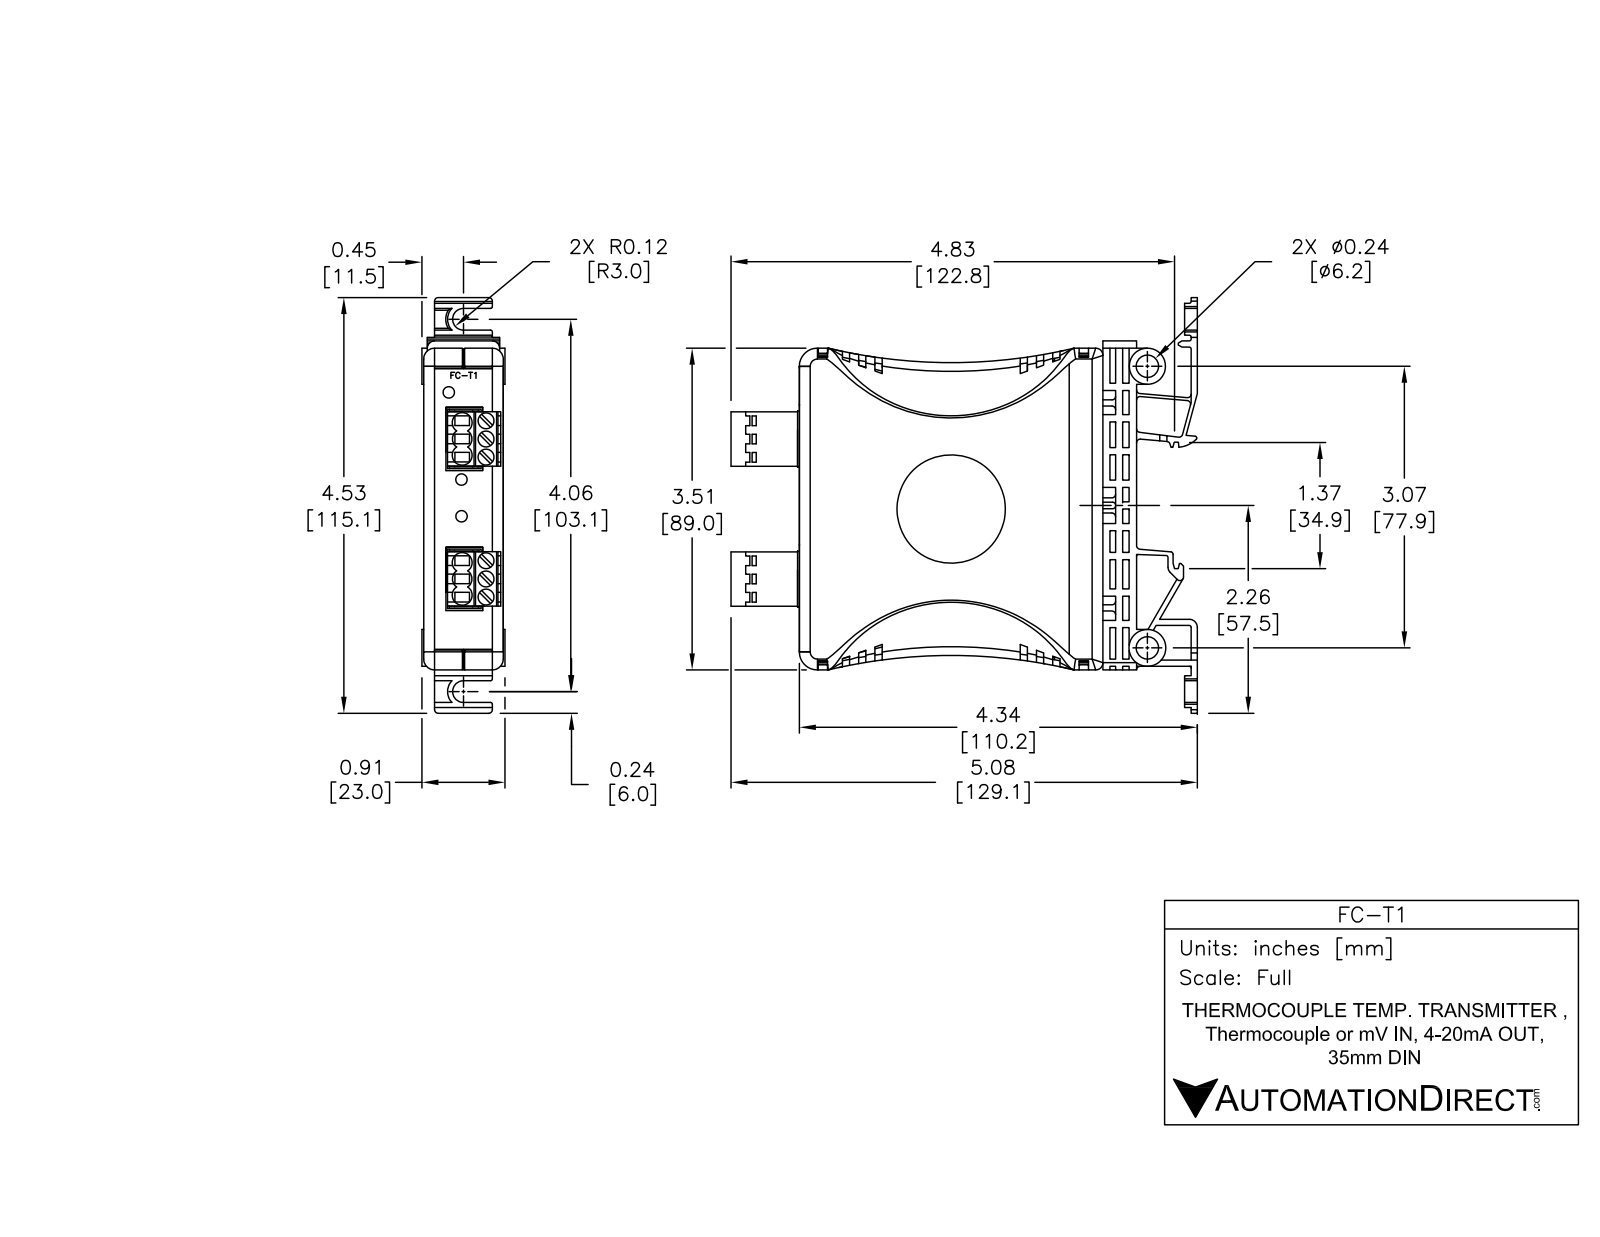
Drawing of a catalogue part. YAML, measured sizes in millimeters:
part_name: "FC-ISO-C r1b Case Only 1 red1 fXT -surf1 - internals COMPLETE FC-T1 pre coord"
step_written_by: "SolidWorks 2017 (AUTOMOTIVE_DESIGN)"
units: millimeters
bodies: {solids: 13, faces: 2341, planar: 1747, cylindrical: 374, other: 220}
overall_size: [115.5, 110.2, 23.6]
volume: 59780
surface_area: 78000
round_holes:
  - {diameter: 0.3, count: 6}
  - {diameter: 0.4, count: 4}
  - {diameter: 3.1, count: 3}
  - {diameter: 1.1, count: 2}
  - {diameter: 1.1, count: 2}
  - {diameter: 6.2, count: 2}
  - {diameter: 30, count: 1}
round_bosses_or_shafts:
  - {diameter: 1.8, count: 6}
  - {diameter: 3, count: 4}
  - {diameter: 13.2, count: 1}
  - {diameter: 10.2, count: 1}
  - {diameter: 10, count: 1}
partial_cylinders:
  - {radius: 0.3, count: 28}
  - {radius: 0.5, count: 23}
  - {radius: 0.4, count: 16}
  - {radius: 1, count: 15}
  - {radius: 1.4, count: 10}
  - {radius: 3, count: 8}
  - {radius: 3.5, count: 6}
  - {radius: 148.1, count: 6}
face_to_face_distances: [1.6, 20.4, 1.5, 15.8, 17.4, 15.7, 14.2, 18.8, 4.5, 3]
hole_center_spacings: [5, 38.8, 10, 10.8, 33.8, 35, 40.1, 43.7]
